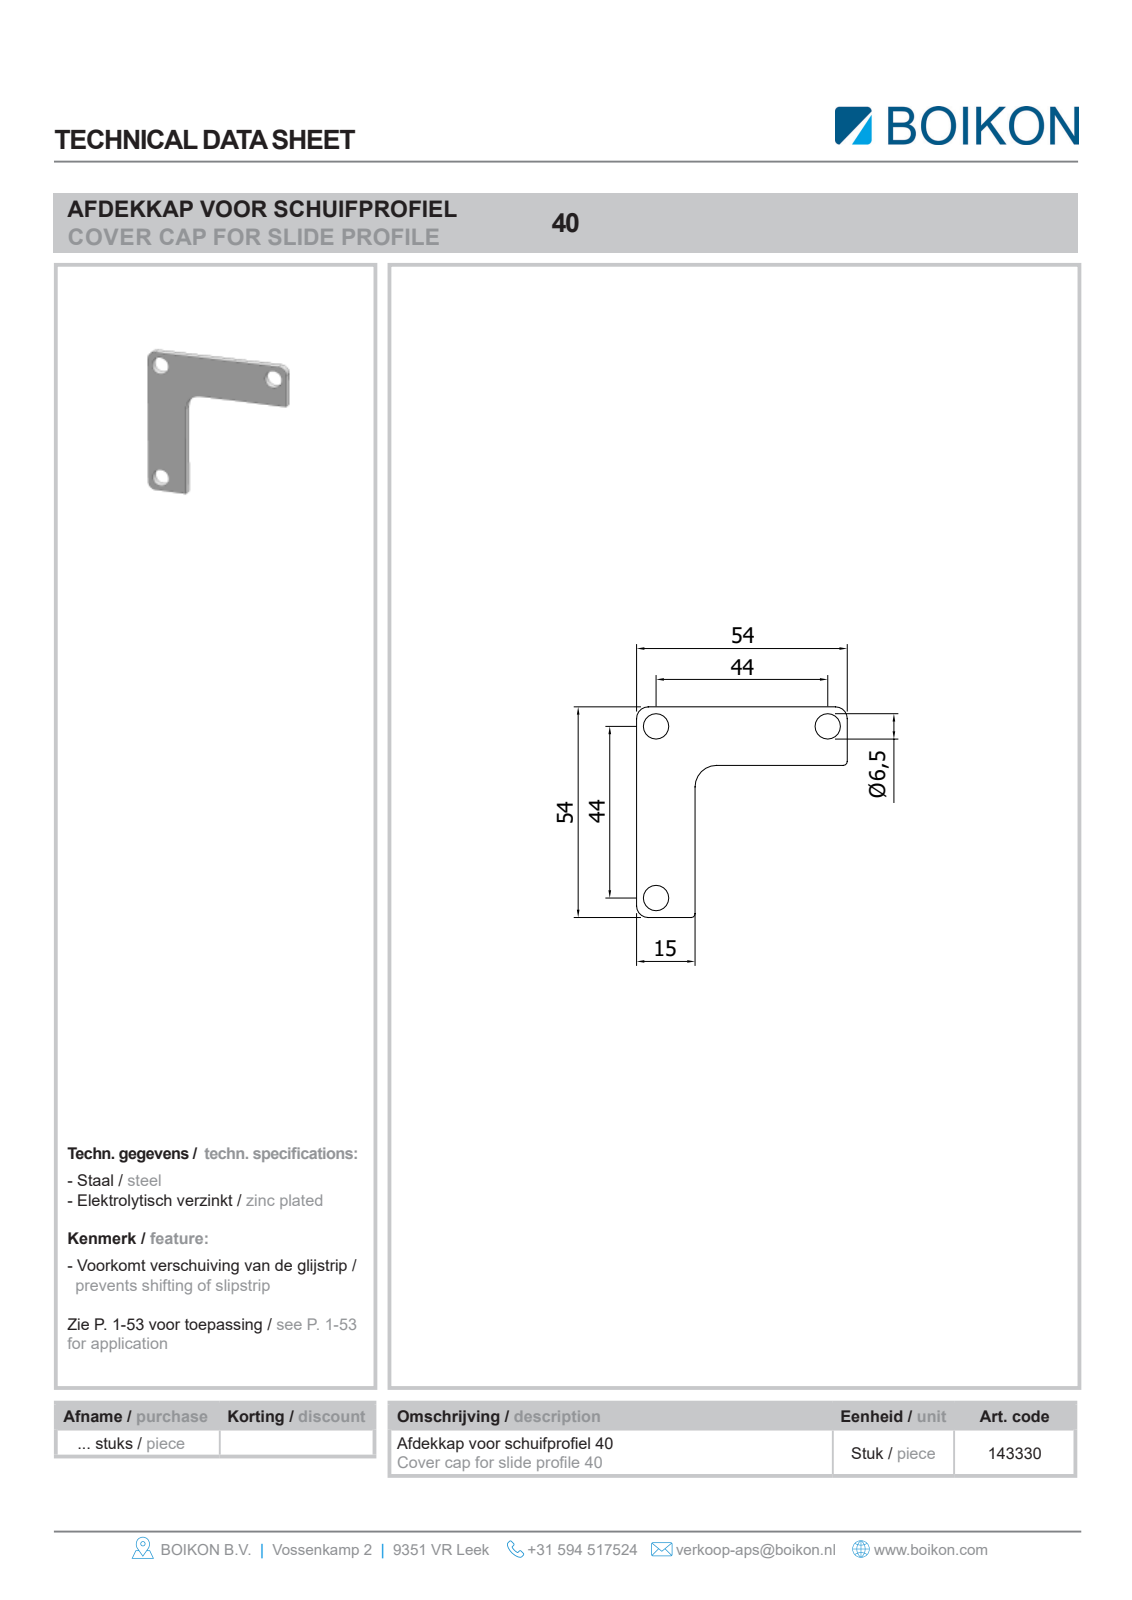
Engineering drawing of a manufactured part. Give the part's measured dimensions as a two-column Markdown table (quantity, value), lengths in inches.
| quantity | value |
| --- | --- |
| part name | Root; 143330Afdekkap voor schuifprofiel 40BOIKON0; 120030Laagbolkopschroef M6 x 16Pan head bolts0 |
| STEP written by | HiCAD 2013 1802.4 Build 509 (AUTOMOTIVE_DESIGN) |
| units | inches |
| bodies | 4 solids, 57 faces (38 planar, 13 cylindrical, 6 other) |
| overall size | 2.146 × 2.146 × 0.76 |
| volume | 0.323 in³ |
| surface area | 7.541 in² |
| round holes (diameter × count) | 0.256 × 3 |
| round bosses / shafts (diameter × count) | 0.236 × 3, 0.188 × 3 |
| partial cylindrical surfaces (radius × count) | 0.118 × 3, 0.217 × 1 |
| main face-to-face distances | 0.118, 0.591, 1.535, 2.126, 0.512, 0.63, 0.157, 0.678, 0.166, 0.048 |
| hole center spacings | 1.732, 2.45 |
